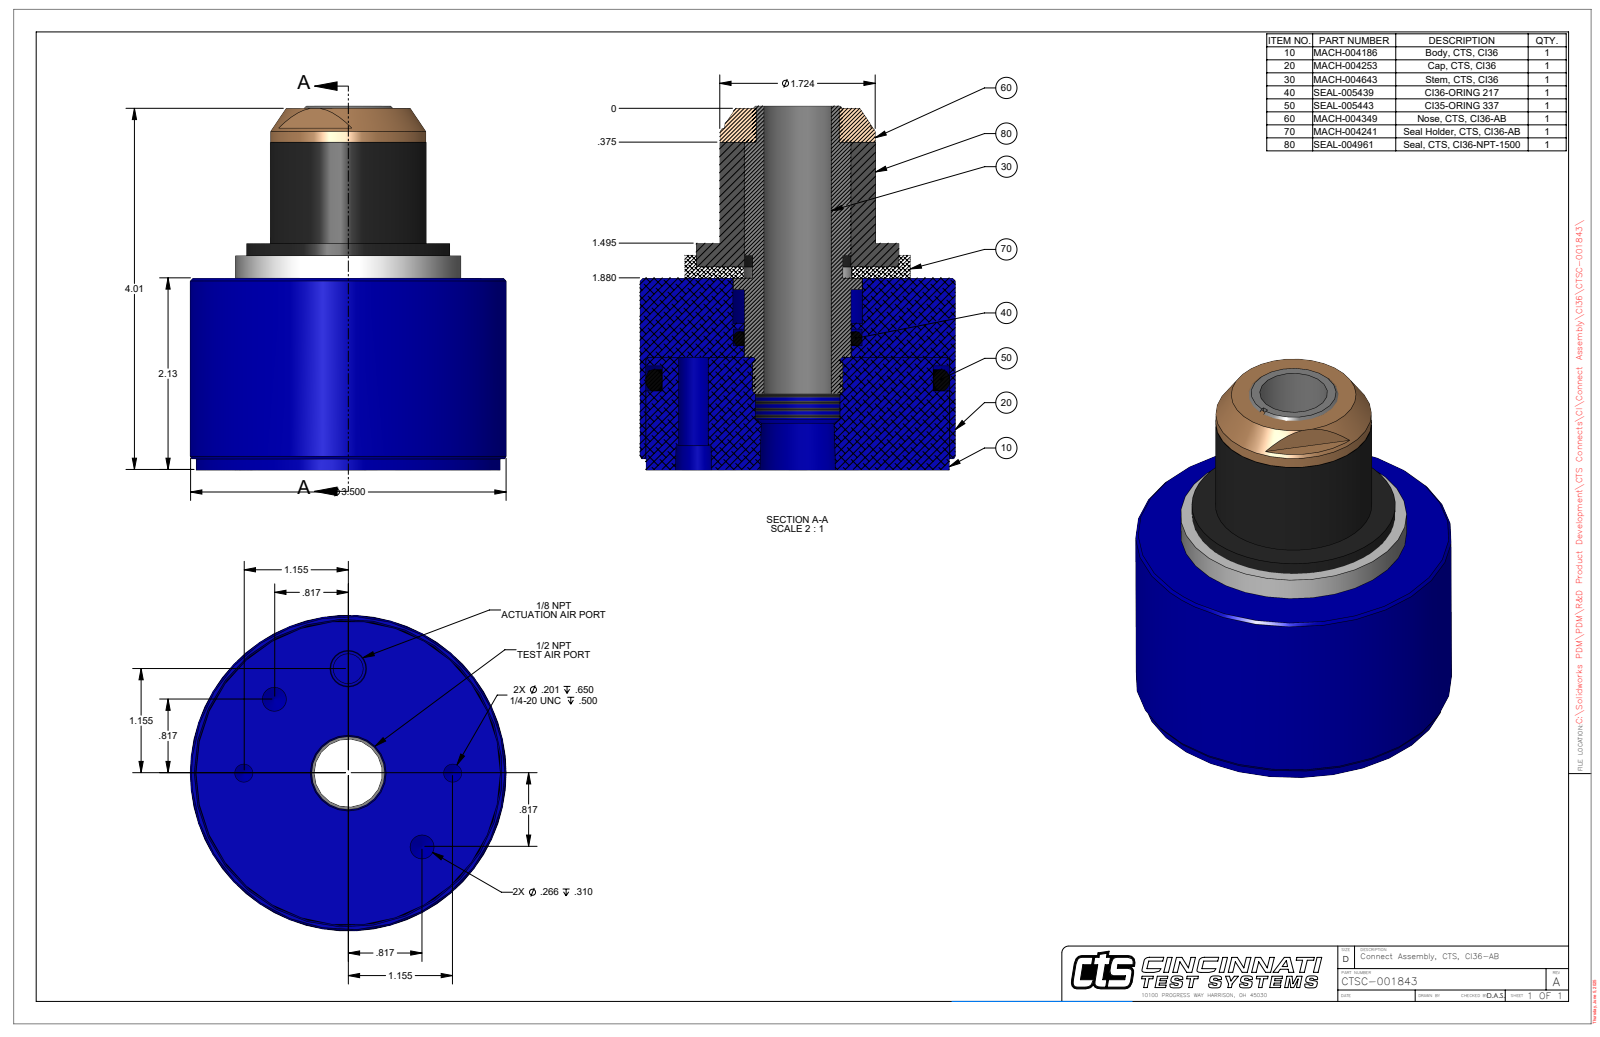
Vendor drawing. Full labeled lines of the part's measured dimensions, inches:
Part name (STEP PRODUCT): CTSC-001843
STEP written by: SolidWorks 2023 (AUTOMOTIVE_DESIGN)
Units: inches
Bodies: 1 solid, 83 faces (24 planar, 35 cylindrical, 24 other)
Overall size (bounding box): 4.032 × 3.5 × 3.5
Volume: 23.41 in³ · Surface area: 79.65 in²
Round holes (diameter × count): ⌀0.201 ×2, ⌀0.266 ×2, ⌀0.332 ×1, ⌀0.75 ×1, ⌀0.937 ×1, ⌀1.438 ×1, ⌀3.373 ×1
Round bosses / shafts (diameter × count): ⌀3.5 ×1, ⌀3.365 ×1, ⌀2.5 ×1, ⌀2.25 ×1, ⌀1.73 ×1, ⌀1.724 ×1, ⌀1.427 ×1
Partial cylindrical surfaces — rounded edges, fillets, slot ends (radius × count): R0.461 ×1, R0.69 ×1
Main face-to-face distances: 2.125, 2.51, 0.385, 2.375, 0.25, 0.135, 4.005, 1.88, 1.63, 1.495
Hole centre spacings: 0.884, 1.155, 2.134, 1.155, 1.633, 2.309, 2.31
